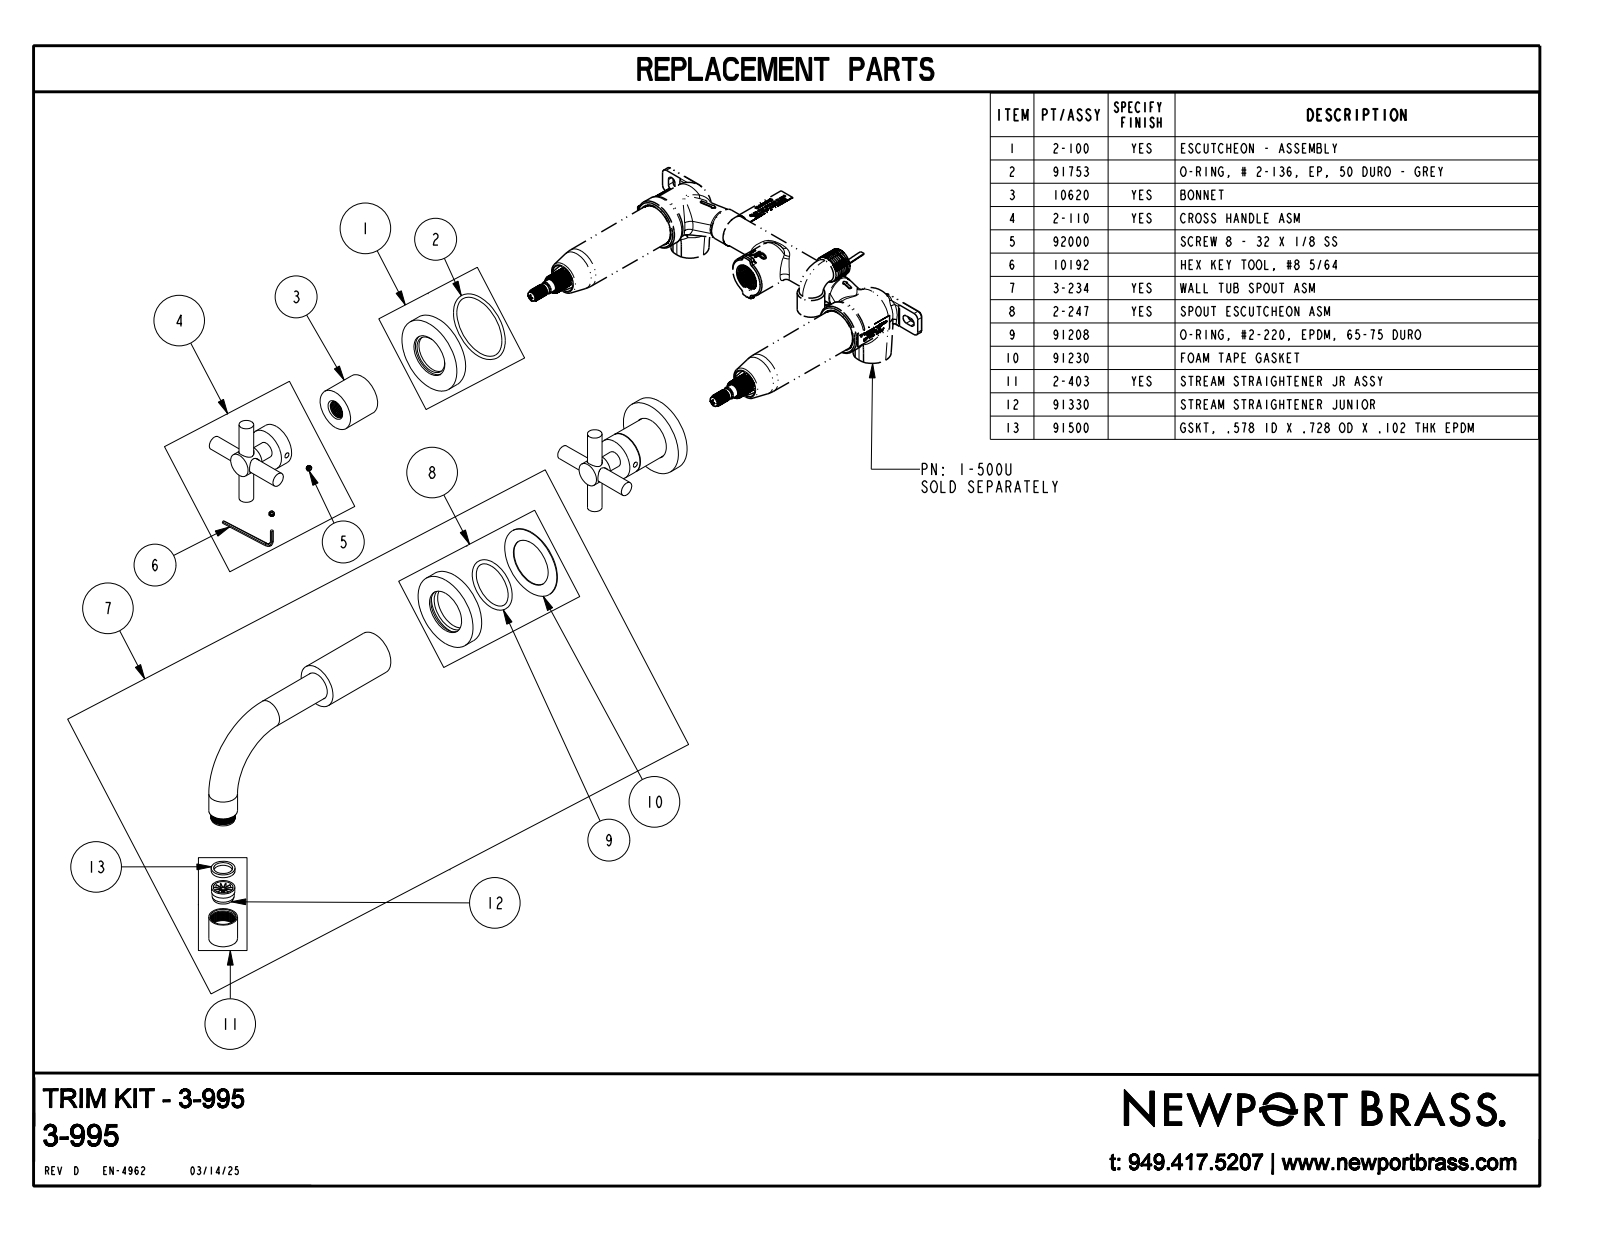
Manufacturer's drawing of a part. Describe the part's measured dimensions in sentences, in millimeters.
The part is named "3-995_SW0002". Its 3-D file was written by "CREO PARAMETRIC BY PTC INC, 2018400 (AUTOMOTIVE_DESIGN)". It is 5 solids with 72 faces: 26 planar, 44 cylindrical and 2 other. Overall it measures 274.7 by 269.9 by 152.3 millimeters. Its volume is 276 100 cubic millimeters and its surface area 60 230 square millimeters. Round bosses or shafts: 3 of diameter 60.3, 3 of diameter 11.3, 2 of diameter 33.4, 2 of diameter 22.2, 2 of diameter 19.1, 2 of diameter 12.7, 1 of diameter 34.9. The main face-to-face distances are 9.5, 37.7, 38.2, 28.1, 28.7, 0.5, 49.4, 39.8, 11.7, 11.2.
